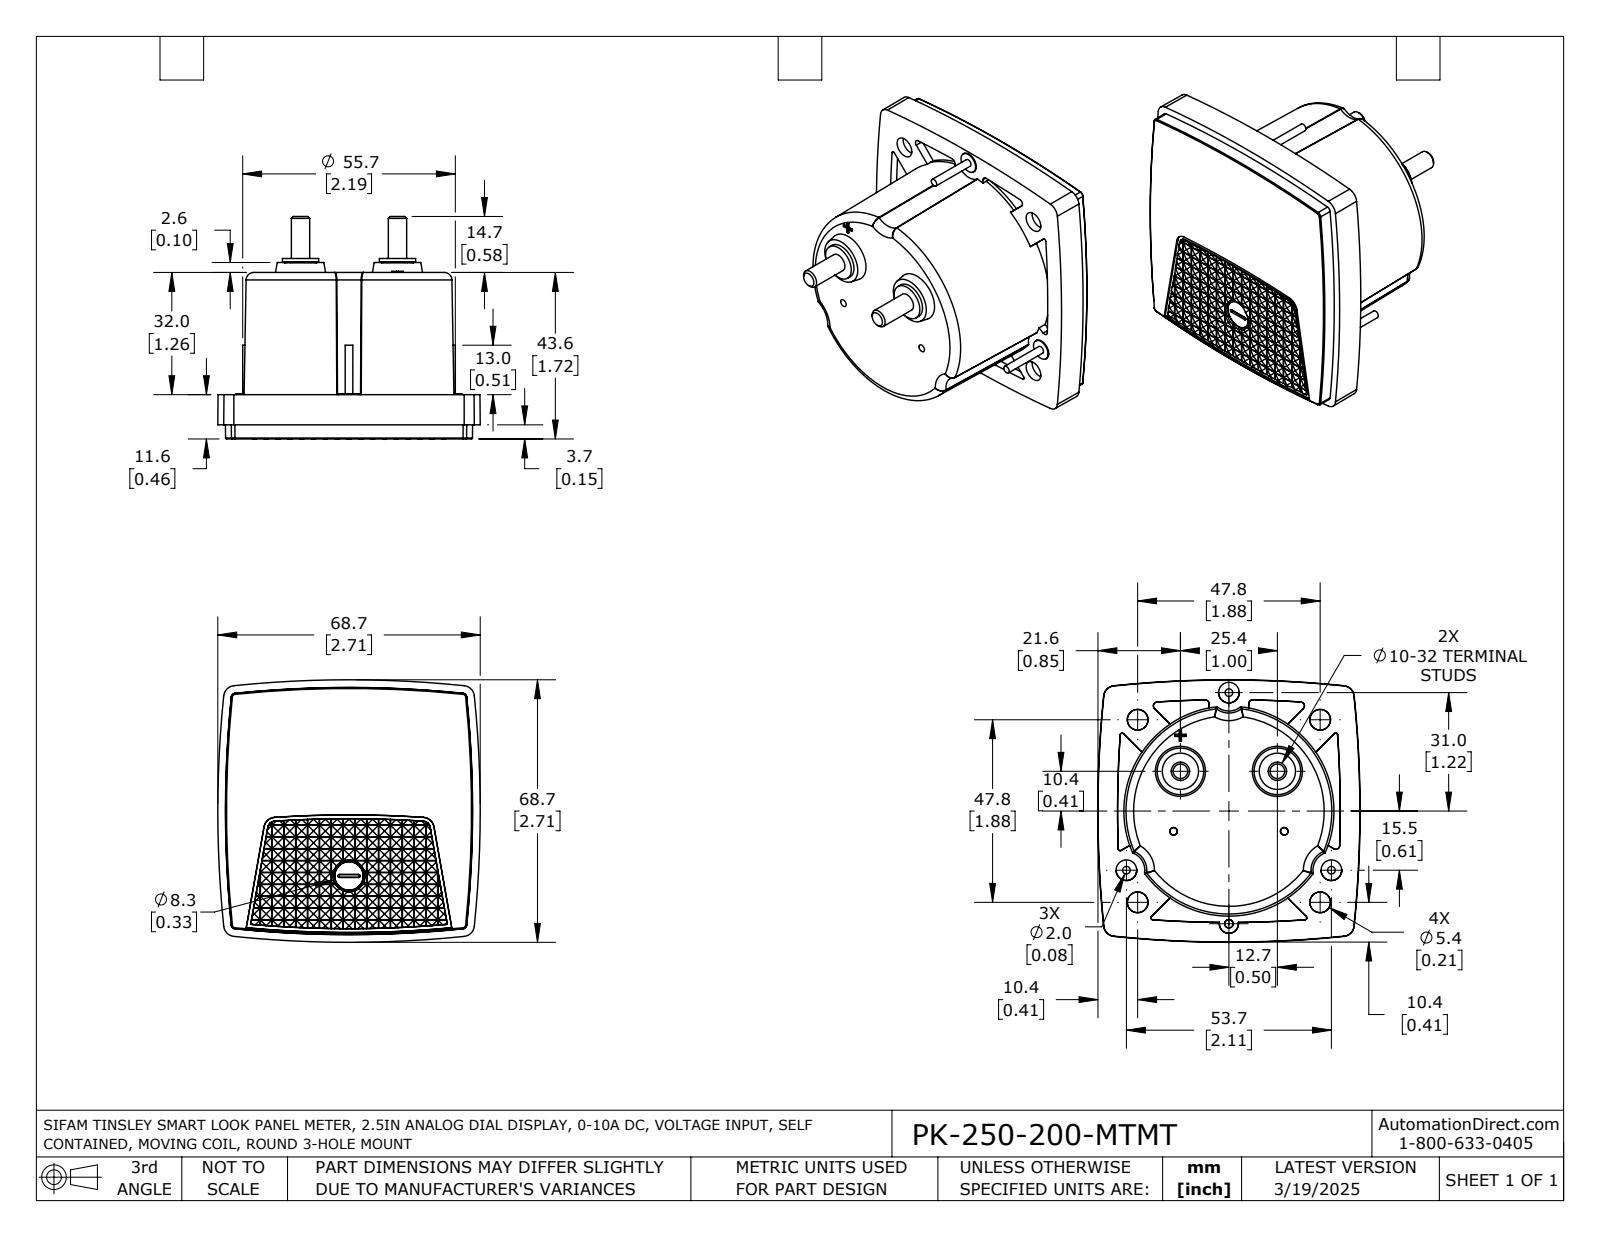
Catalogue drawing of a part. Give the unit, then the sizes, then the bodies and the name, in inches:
Units: inches
Overall size (bounding box): 2.706 × 2.706 × 2.297
Round bosses / shafts (diameter × count): ⌀0.213 ×3, ⌀0.079 ×3, ⌀0.374 ×2, ⌀0.189 ×2, ⌀0.215 ×1
Partial cylindrical surfaces — rounded edges, fillets, slot ends (radius × count): R0.167 ×2, R1.083 ×1
Main face-to-face distances: 1.717, 1.26, 0.457, 0.024, 0.087, 0.096, 0.311, 0.12, 0.072, 1.346
Volume: 7.594 in³ · Surface area: 30.41 in²
Bodies: 1 solid, 1550 faces (1165 planar, 265 cylindrical, 120 other)
Part name (STEP PRODUCT): PK-250-200-MTMT
STEP written by: SolidWorks 2021 (AUTOMOTIVE_DESIGN)
